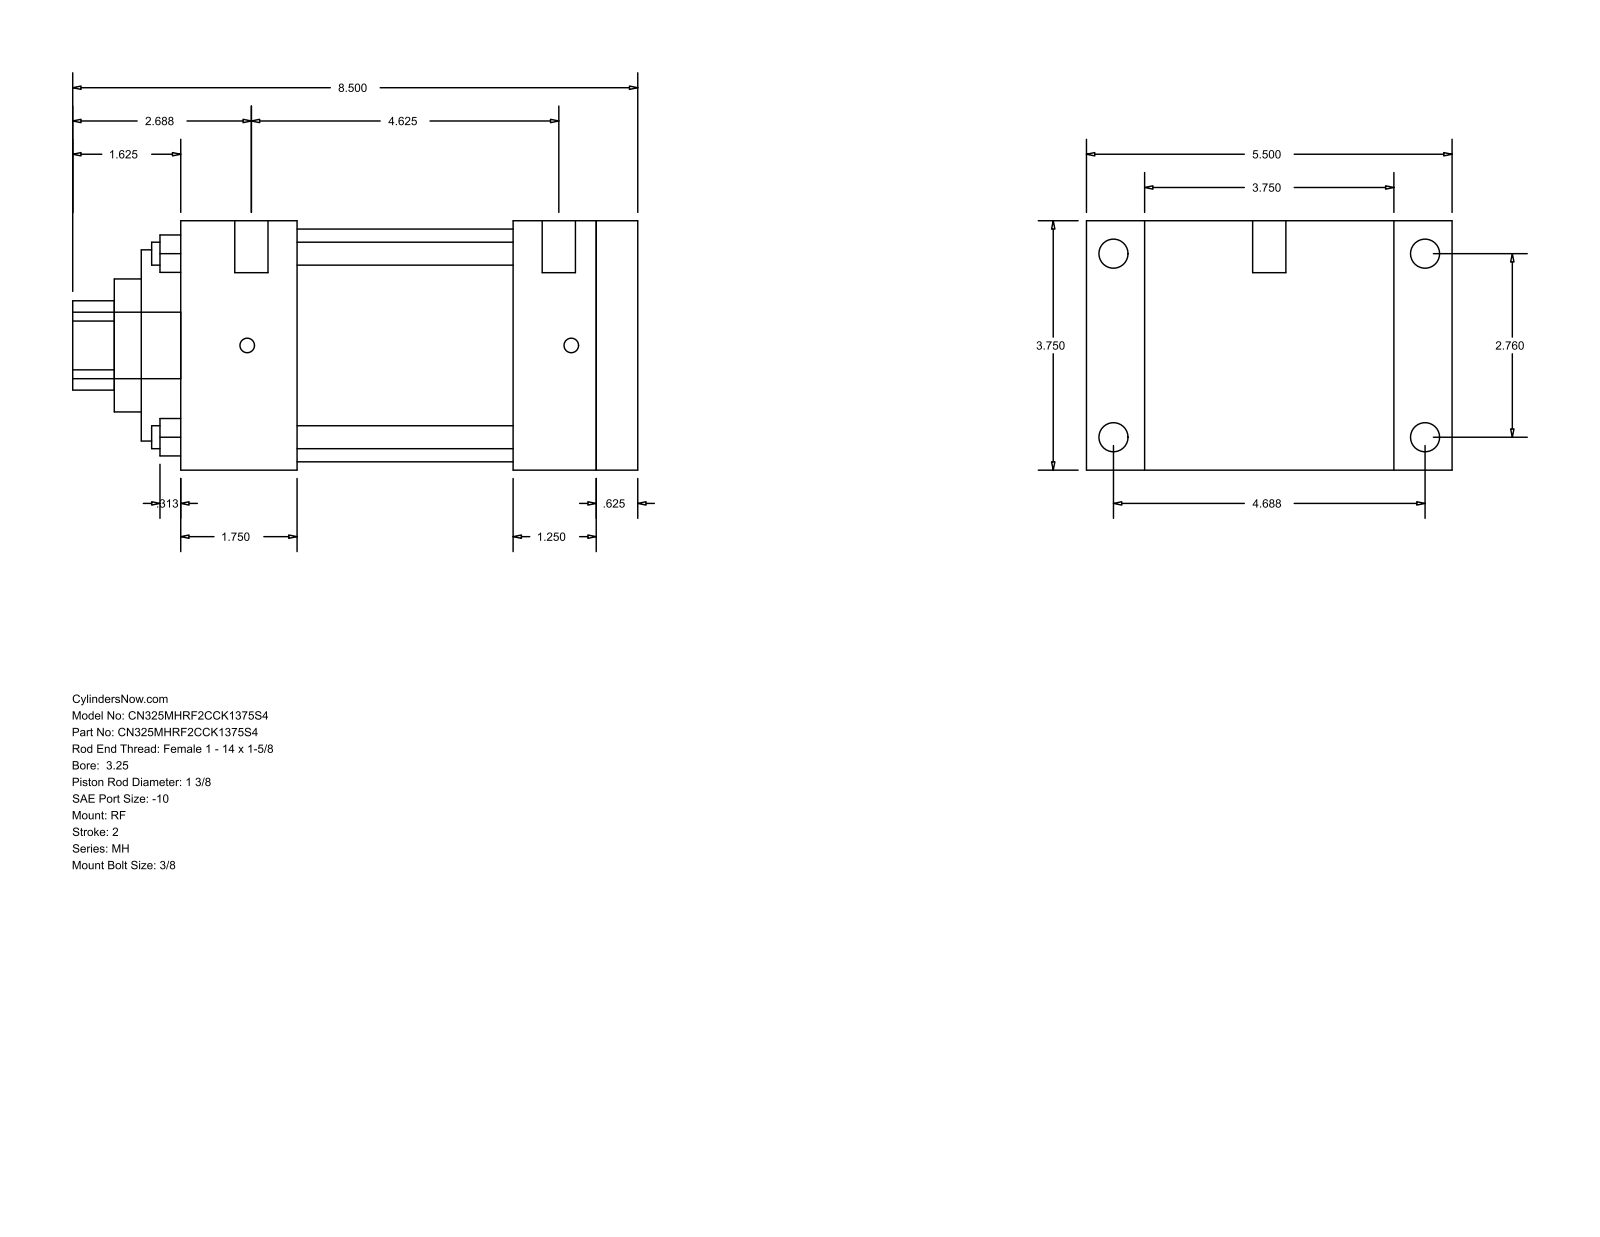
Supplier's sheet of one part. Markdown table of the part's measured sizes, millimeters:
| quantity | value |
| --- | --- |
| part name | MH_RF__0325_1.375 |
| STEP written by | GSSL Pune (CONFIG_CONTROL_DESIGN) |
| units | millimeters |
| bodies | 0 solids, 94 faces (65 planar, 29 cylindrical, 0 other) |
| overall size | 215.9 × 139.7 × 95.25 |
| round holes (diameter × count) | 8.76 × 4, 34.92 × 1, 50.8 × 1, 73.03 × 1, 88.9 × 1 |
| round bosses / shafts (diameter × count) | 11.13 × 4, 5.56 × 4, 12.7 × 2, 25.4 × 1 |
| partial cylindrical surfaces (radius × count) | 17.06 × 1 |
| main face-to-face distances | 95.24, 174.63, 158.76, 15.87, 22.23, 117.47, 44.45, 114.31, 130.18, 127.01 |
| hole center spacings | 49.57, 70.1, 99.14 |
